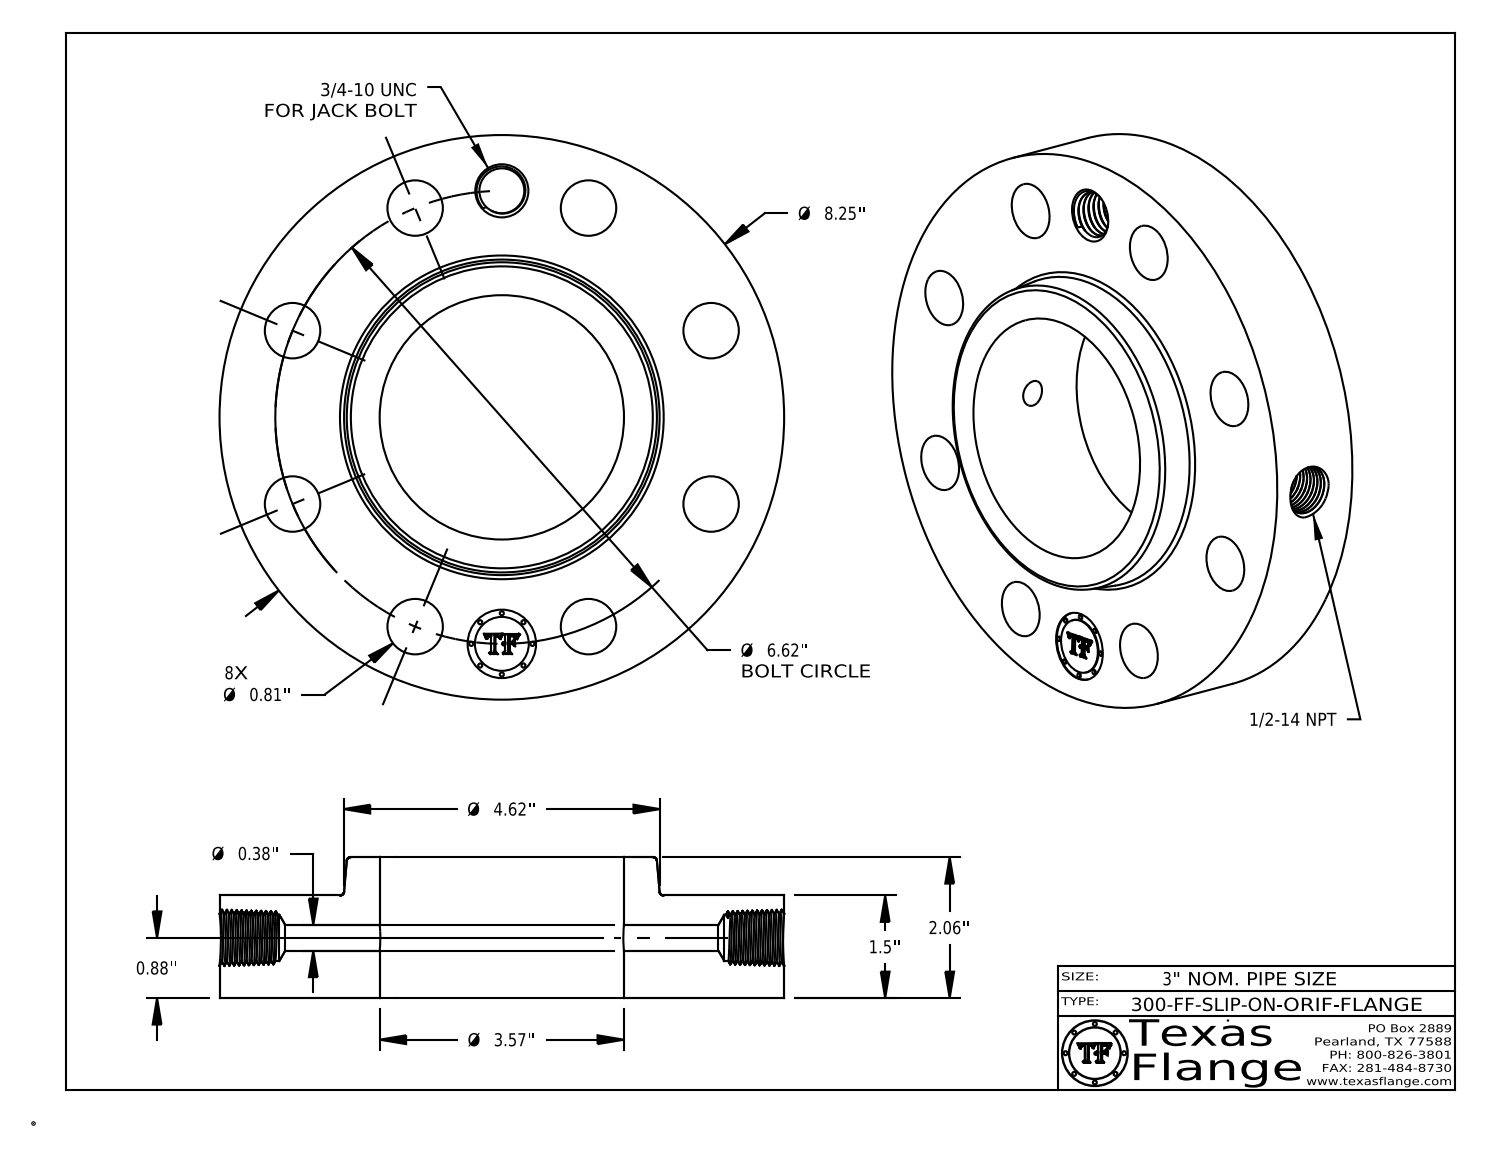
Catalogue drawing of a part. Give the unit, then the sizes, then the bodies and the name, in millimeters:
Units: millimetres
Overall size (bounding box): 209.6 × 209.6 × 52.3
Round holes (diameter × count): ⌀20.6 ×8, ⌀9.5 ×1, ⌀16.7 ×1, ⌀17.1 ×1, ⌀25.4 ×1, ⌀90.7 ×1
Round bosses / shafts (diameter × count): ⌀1.5 ×8, ⌀209.6 ×1, ⌀20 ×1
Main face-to-face distances: 38.1, 52.3, 14.2, 0.4, 37.7, 14.6, 7.6, 7.4, 1.4, 6.3
Hole centre spacings: 84.1, 118.9, 155.3, 168.1, 32.8, 64.3, 64.3, 93.4
Volume: 998 000 mm³ · Surface area: 123 700 mm²
Bodies: 1 solid, 764 faces (368 planar, 88 cylindrical, 308 other)
Part name (STEP PRODUCT): 300-FF-SLIP-ON
STEP written by: CATIA V5 STEP AP214 (AUTOMOTIVE_DESIGN)
